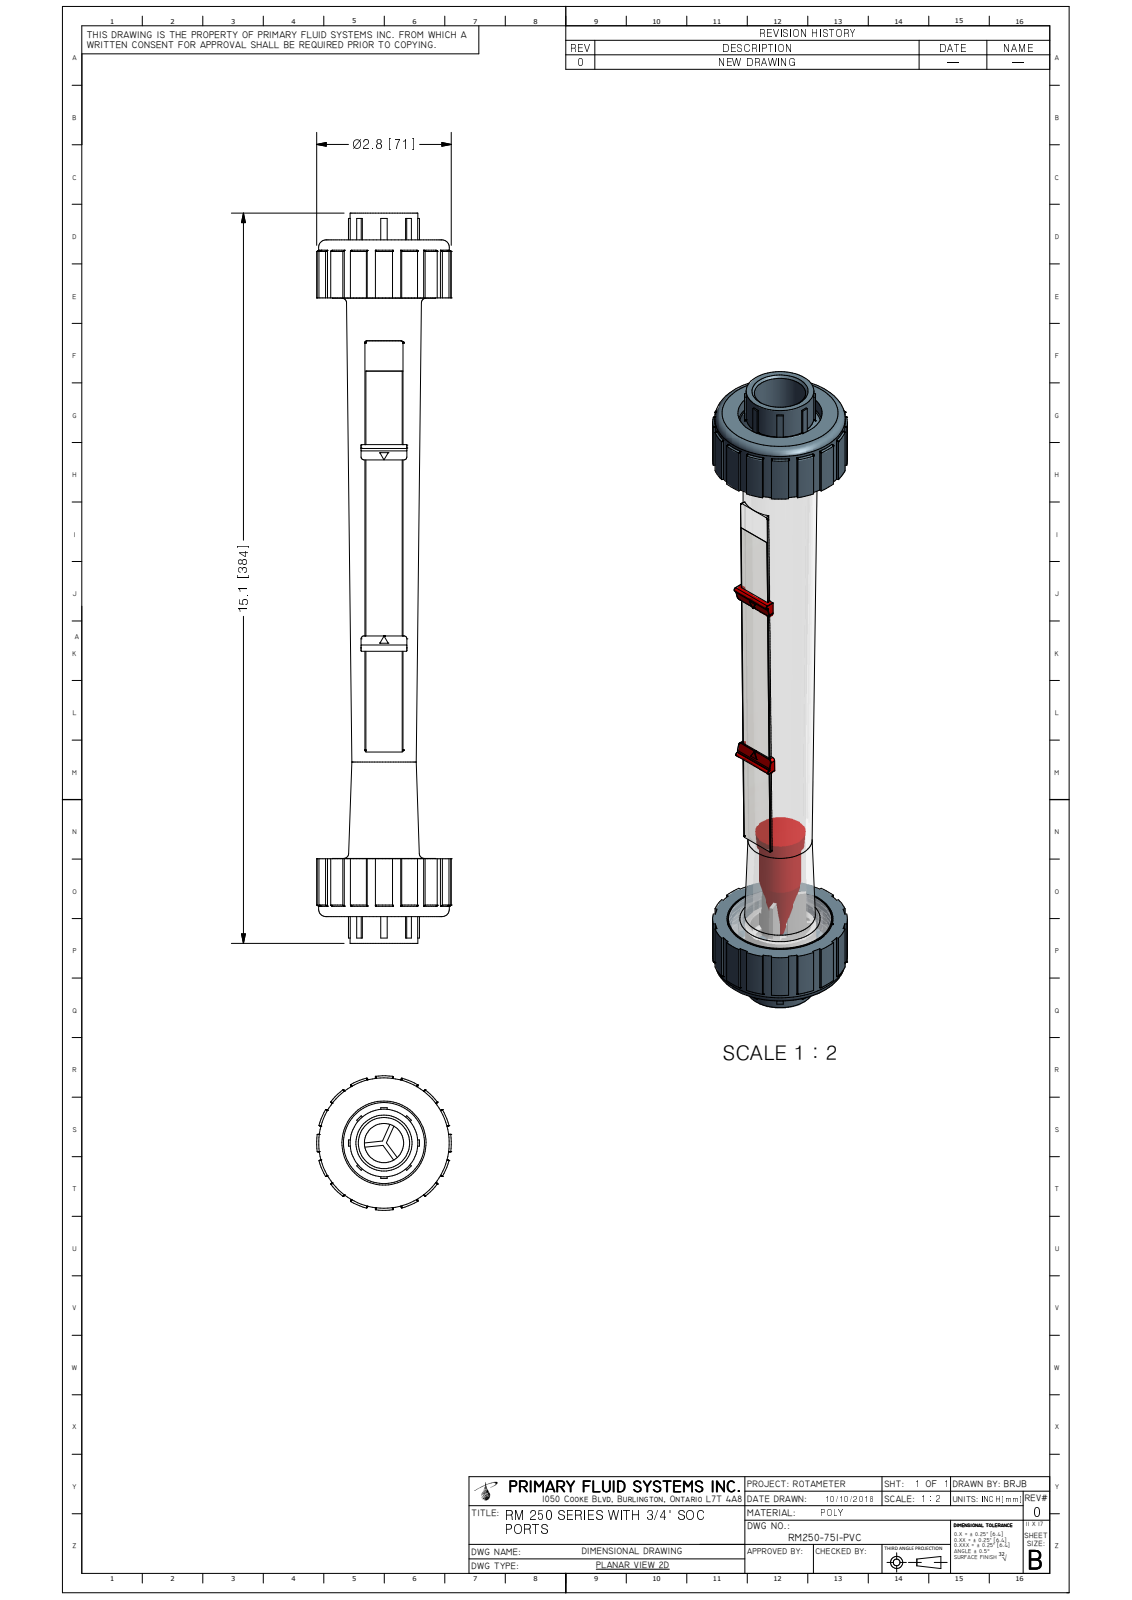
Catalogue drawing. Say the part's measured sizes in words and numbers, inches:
The part is named "RM250-75I-PVC_R0". Its 3-D file was written by "Autodesk Inventor 2009 (AUTOMOTIVE_DESIGN)". It is 1 solid with 587 faces: 262 planar, 126 cylindrical and 199 other. Overall it measures 15.1 by 2.783 by 2.783 inches. Its volume is 31.99 cubic inches and its surface area 168.3 square inches. Round holes: 1 of diameter 1.058, 1 of diameter 1.738, 1 of diameter 2.19. Round bosses or shafts: 1 of diameter 2.697, 1 of diameter 2.152, 1 of diameter 2.026, 1 of diameter 1.485, 1 of diameter 1.4. Partial cylindrical surfaces (rounded edges, fillets, slot ends): 18 of radius 0.008, 16 of radius 0.01, 10 of radius 0.004, 4 of radius 0.006, 4 of radius 0.06, 2 of radius 0.008, 2 of radius 0.04, 2 of radius 0.045. The main face-to-face distances are 1.197, 12.795, 1.205, 12.787, 11.59, 0.496, 13.496, 0.701, 12.299, 12.291.
